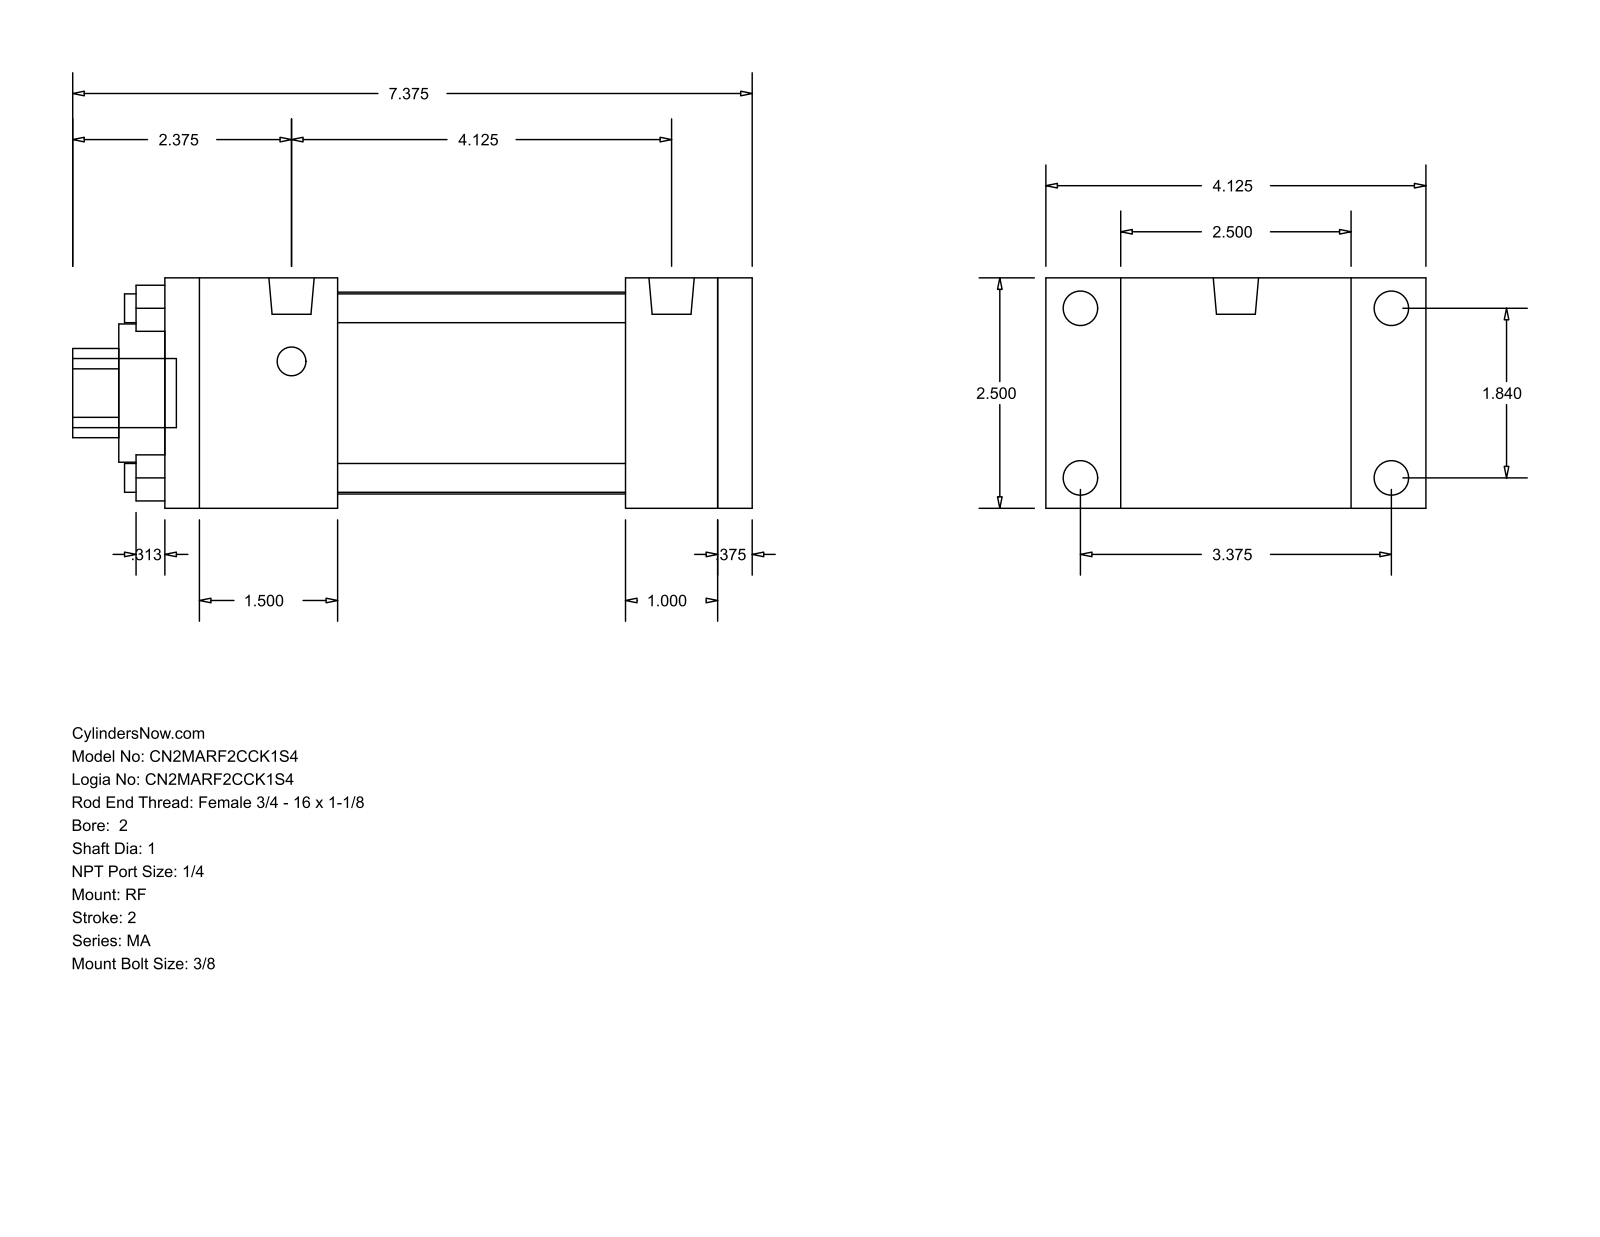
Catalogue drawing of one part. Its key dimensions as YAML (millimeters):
part_name: "MA_RF__0200_1"
step_written_by: "GSSL Pune (CONFIG_CONTROL_DESIGN)"
units: millimeters
bodies: {solids: 0, faces: 92, planar: 64, cylindrical: 28, other: 0}
overall_size: [187.32, 104.78, 63.5]
round_holes:
  - {diameter: 7.94, count: 4}
  - {diameter: 25.4, count: 1}
  - {diameter: 38.1, count: 1}
  - {diameter: 55.63, count: 1}
round_bosses_or_shafts:
  - {diameter: 9.53, count: 4}
  - {diameter: 7.94, count: 4}
  - {diameter: 12.49, count: 2}
  - {diameter: 19.05, count: 1}
partial_cylinders:
  - {radius: 12.29, count: 1}
face_to_face_distances: [63.5, 152.4, 9.52, 161.92, 25.4, 20.64, 12.7, 47.63, 104.77, 114.29]
hole_center_spacings: [33.05, 46.74, 66.1]
